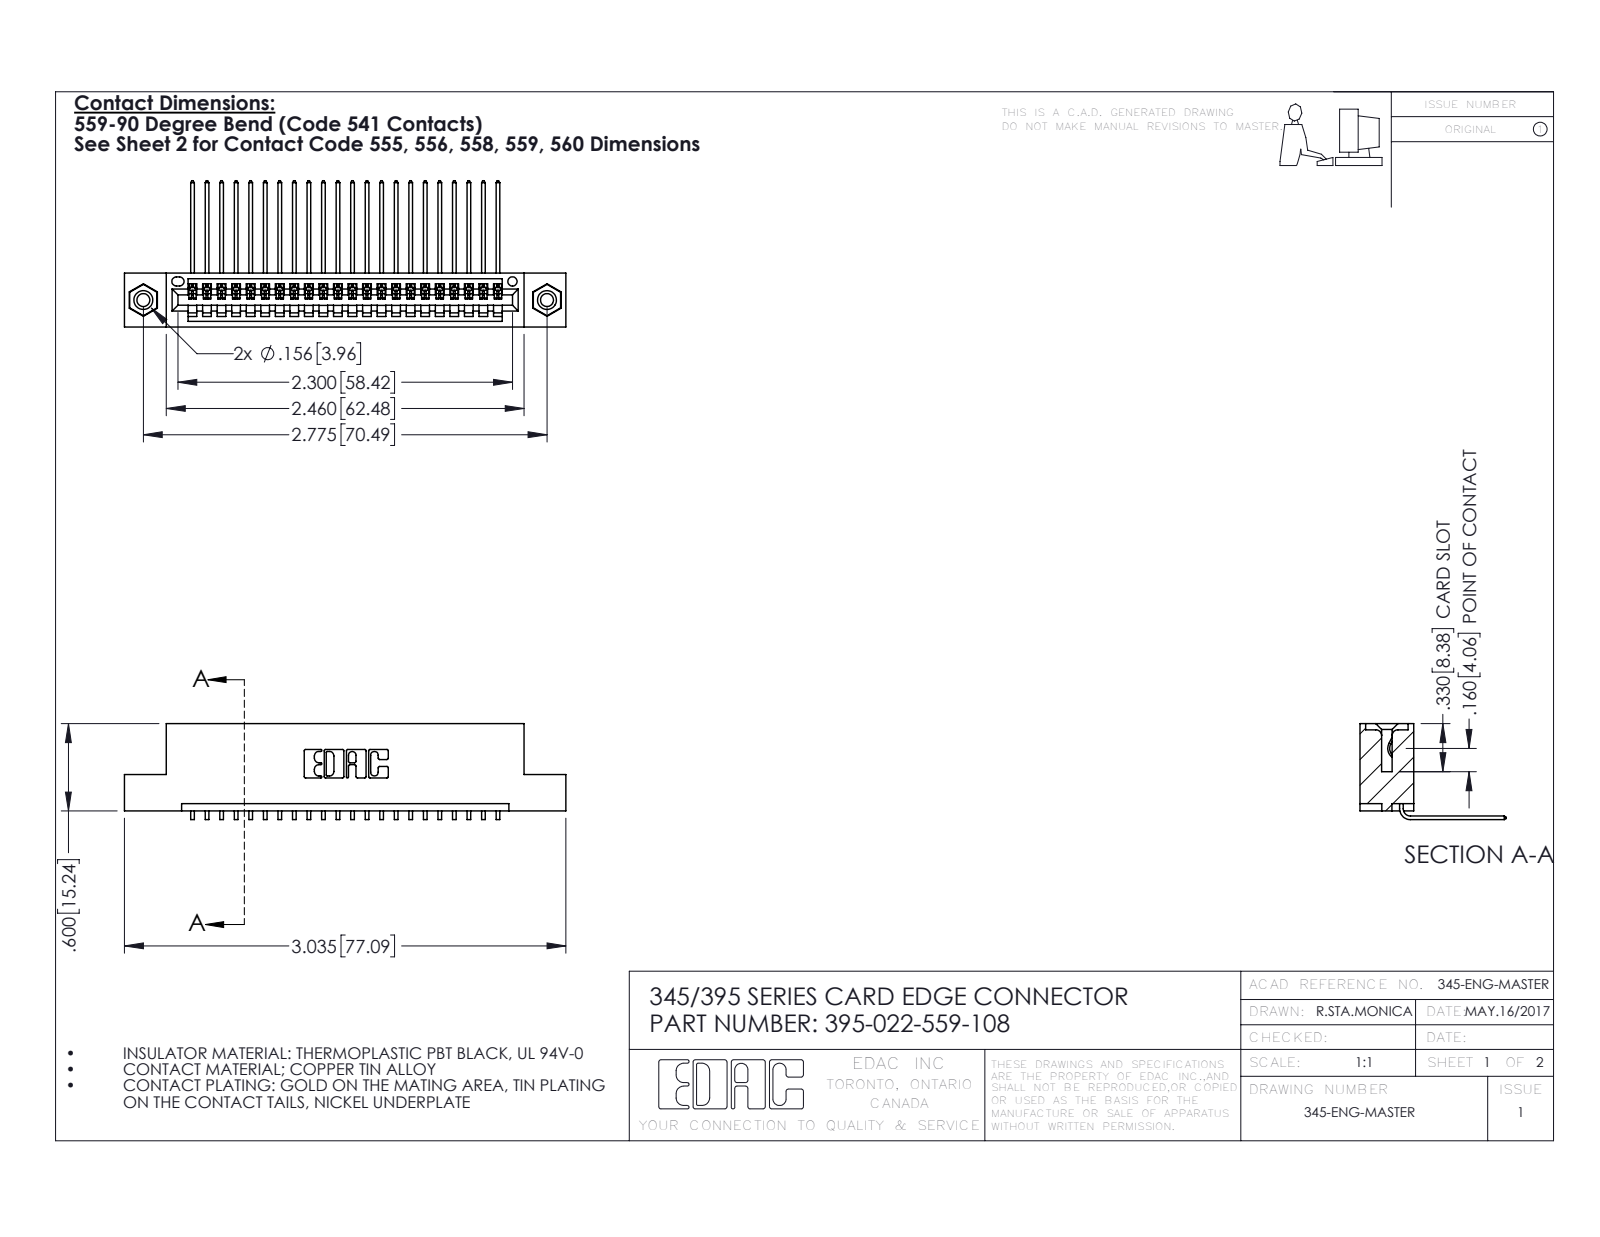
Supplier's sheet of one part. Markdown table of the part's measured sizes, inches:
| quantity | value |
| --- | --- |
| part name | 345 Part_Flush Mounting Lugs - 0.156 Dia-TI; 345-250-001_345-250-003-102; 395-022-559-108; 345-292-001_558 559 Tail - 1 |
| STEP written by | SolidWorks 2016 (CONFIG_CONTROL_DESIGN) |
| units | inches |
| bodies | 25 solids, 1506 faces (1036 planar, 454 cylindrical, 16 other) |
| overall size | 3.035 × 1.005 × 0.659 |
| volume | 0.441 in³ |
| surface area | 15.16 in² |
| round holes (diameter × count) | 0.089 × 2, 0.125 × 2, 0.156 × 2, 0.064 × 1 |
| round bosses / shafts (diameter × count) | 0.155 × 2 |
| partial cylindrical surfaces (radius × count) | 0.006 × 44, 0.01 × 22, 0.007 × 6, 0.031 × 6, 0.026 × 3, 0.031 × 2, 0.04 × 2, 0.014 × 1 |
| main face-to-face distances | 0.072, 0.298, 0.37, 0.2, 0.098, 0.272, 0.025, 0.225, 0.149, 0.072 |
| hole center spacings | 0.27, 2.541, 2.775 |
